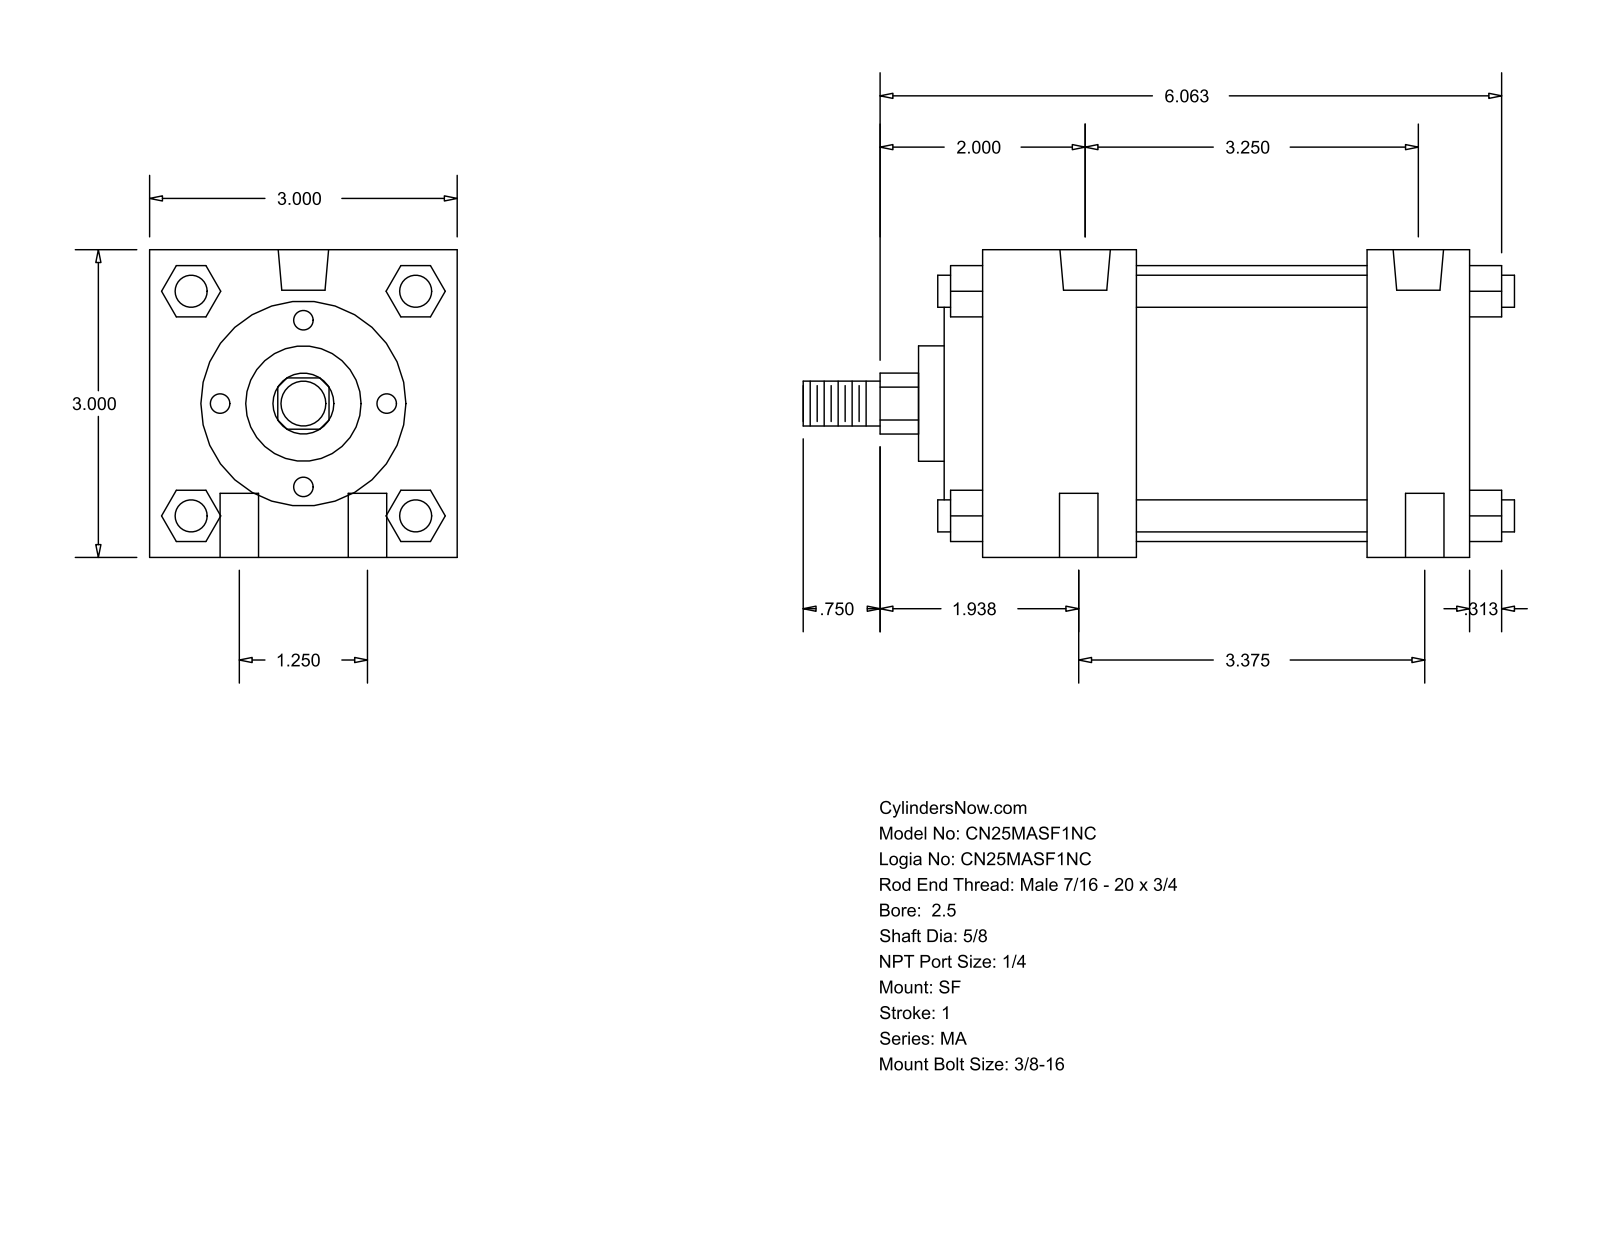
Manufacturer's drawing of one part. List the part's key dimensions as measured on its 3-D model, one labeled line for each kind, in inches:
Part name (STEP PRODUCT): MA_SF__0250_0.625
STEP written by: GSSL Pune (CONFIG_CONTROL_DESIGN)
Units: inches
Bodies: 0 solids, 126 faces (95 planar, 31 cylindrical, 0 other)
Overall size (bounding box): 6.937 × 3 × 3
Round holes (diameter × count): ⌀0.375 ×4, ⌀0.313 ×2, ⌀0.492 ×2
Round bosses / shafts (diameter × count): ⌀0.313 ×4, ⌀2.69 ×1, ⌀2 ×1, ⌀1.125 ×1, ⌀0.625 ×1, ⌀0.437 ×1
Partial cylindrical surfaces — rounded edges, fillets, slot ends (radius × count): R0.297 ×1
Main face-to-face distances: 3, 4.75, 1, 3.25, 2.25, 3.75, 1.5, 0.5, 0.375, 1.875
Hole centre spacings: 0.628, 3.371, 1.25, 3.25, 3.375, 3.599
